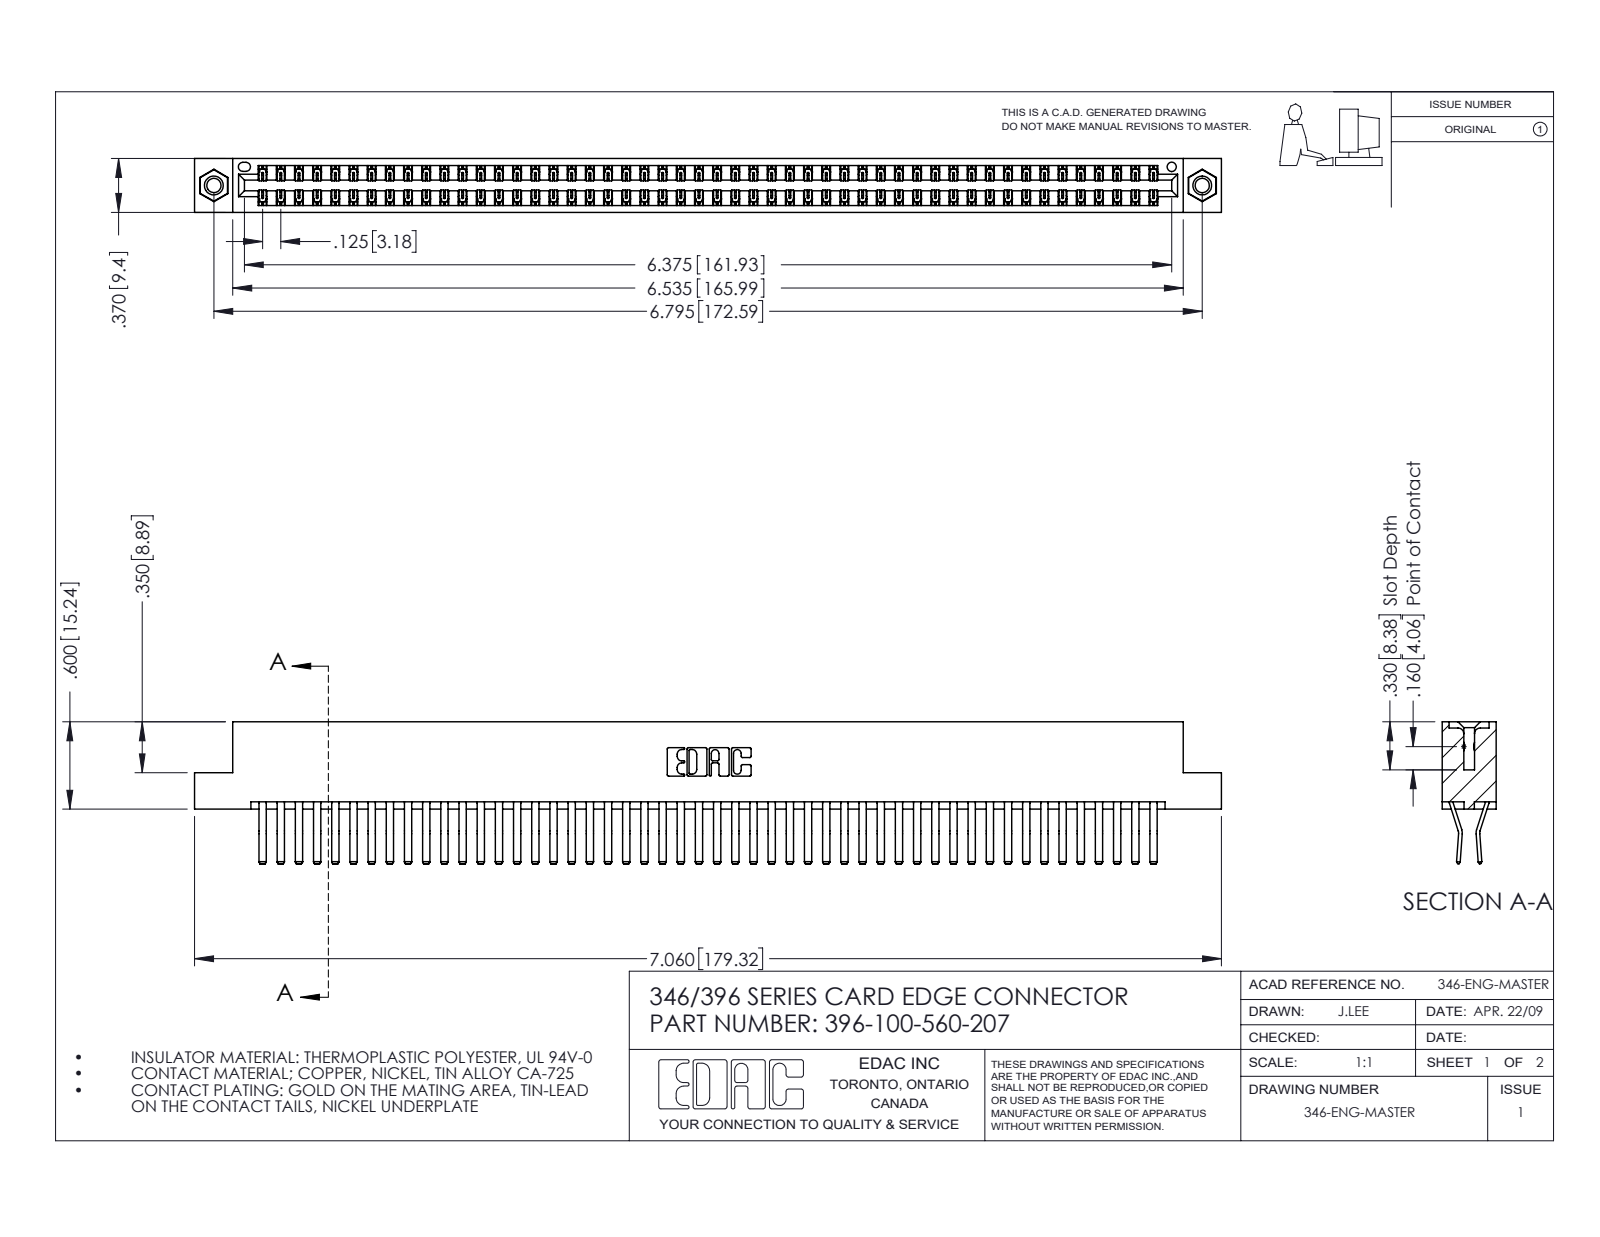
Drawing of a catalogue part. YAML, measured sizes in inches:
part_name: "396-100-560-207; 346 Part_Flush Mounting Lugs - 0.156 Dia-TI; 345-292-001_560 Tail; 345-250-001_345-250-005-103"
step_written_by: "SolidWorks 2016 (CONFIG_CONTROL_DESIGN)"
units: inches
bodies: {solids: 103, faces: 5582, planar: 3608, cylindrical: 1958, other: 16}
overall_size: [7.06, 0.975, 0.37]
volume: 1.11
surface_area: 41.71
round_holes:
  - {diameter: 0.098, count: 2}
  - {diameter: 0.125, count: 2}
  - {diameter: 0.156, count: 2}
  - {diameter: 0.064, count: 1}
round_bosses_or_shafts:
  - {diameter: 0.155, count: 2}
partial_cylinders:
  - {radius: 0.006, count: 150}
  - {radius: 0.01, count: 22}
  - {radius: 0.007, count: 6}
  - {radius: 0.031, count: 6}
  - {radius: 0.026, count: 3}
  - {radius: 0.01, count: 2}
  - {radius: 0.014, count: 2}
  - {radius: 0.022, count: 2}
face_to_face_distances: [0.048, 0.322, 0.37, 0.025, 0.25, 0.072, 0.298, 0.275, 0.148, 0.222]
hole_center_spacings: [0.246, 6.586, 6.795]
